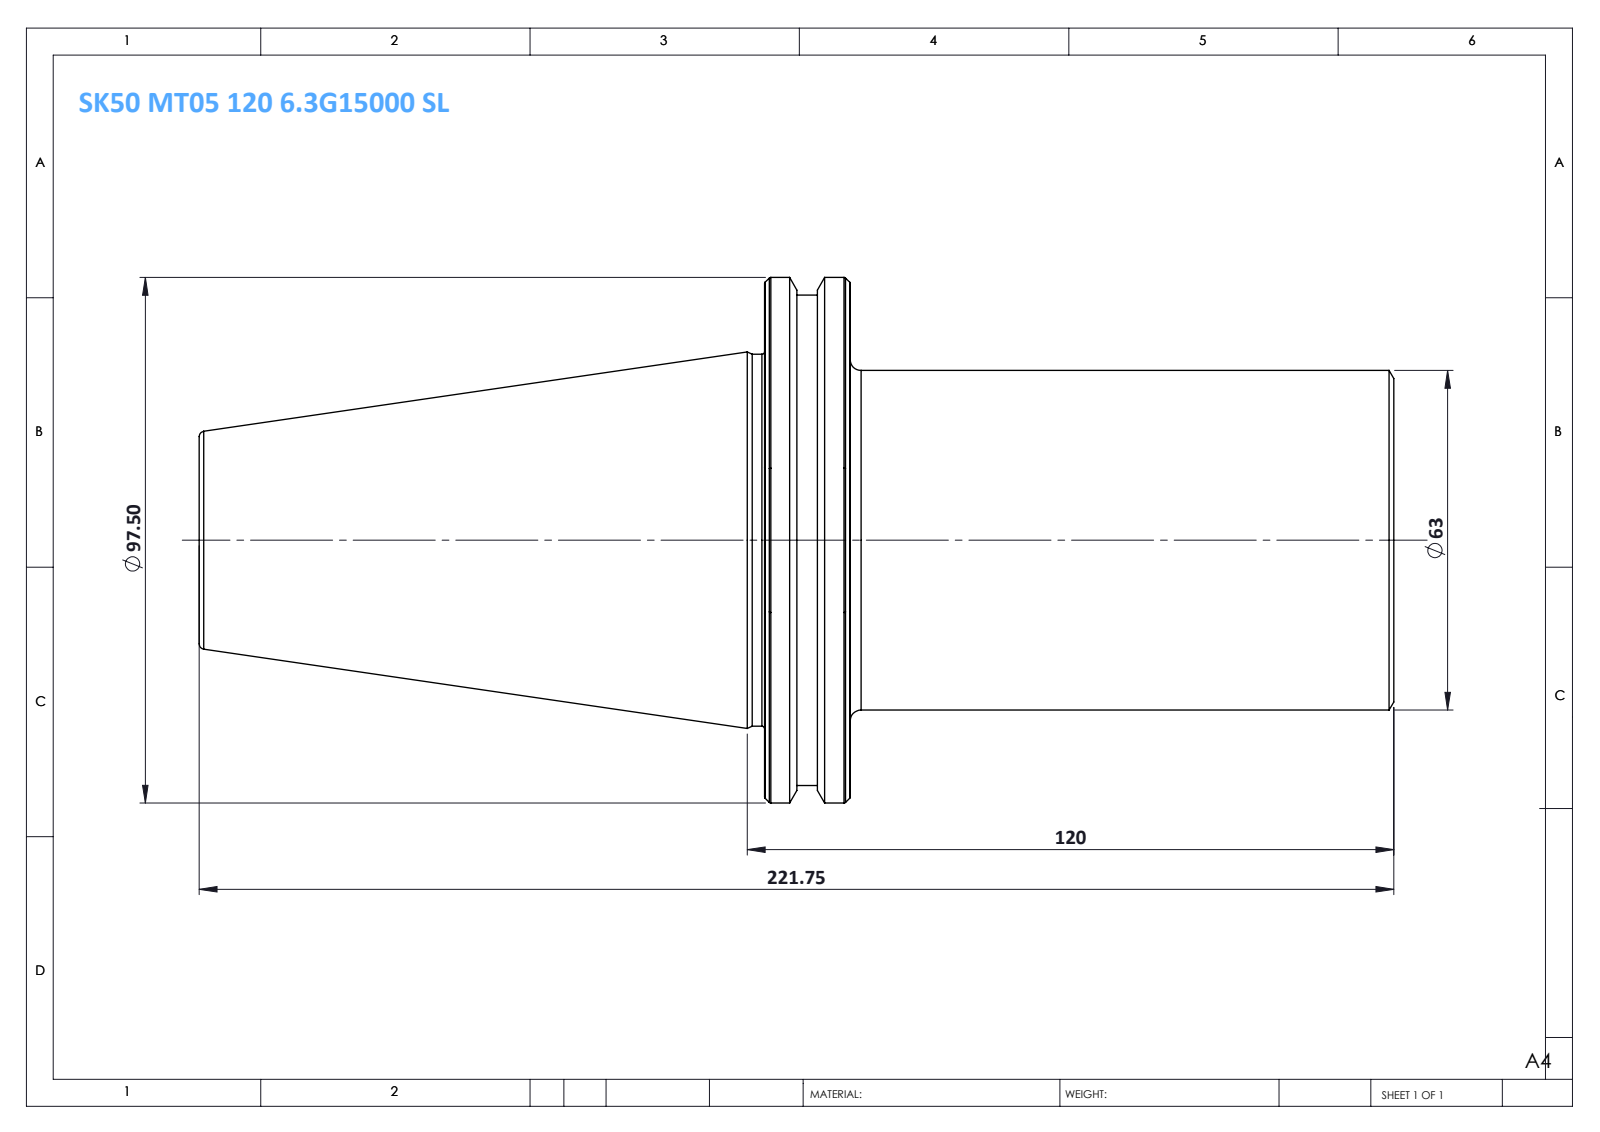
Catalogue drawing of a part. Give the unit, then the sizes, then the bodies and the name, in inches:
Units: inches
Overall size (bounding box): 8.73 × 3.839 × 3.839
Round bosses / shafts (diameter × count): ⌀3.839 ×1, ⌀3.583 ×1, ⌀2.717 ×1, ⌀2.48 ×1
Main face-to-face distances: 0.626, 3.972, 4.598, 8.73, 4.758, 4.132, 4.362, 0.39, 0.236, 4.368
Volume: 41.99 in³ · Surface area: 87.21 in²
Bodies: 1 solid, 64 faces (6 planar, 10 cylindrical, 48 other)
Part name (STEP PRODUCT): SK 50 MT05 120 6.3G15000 SL
STEP written by: SolidWorks 2014 (CONFIG_CONTROL_DESIGN)
